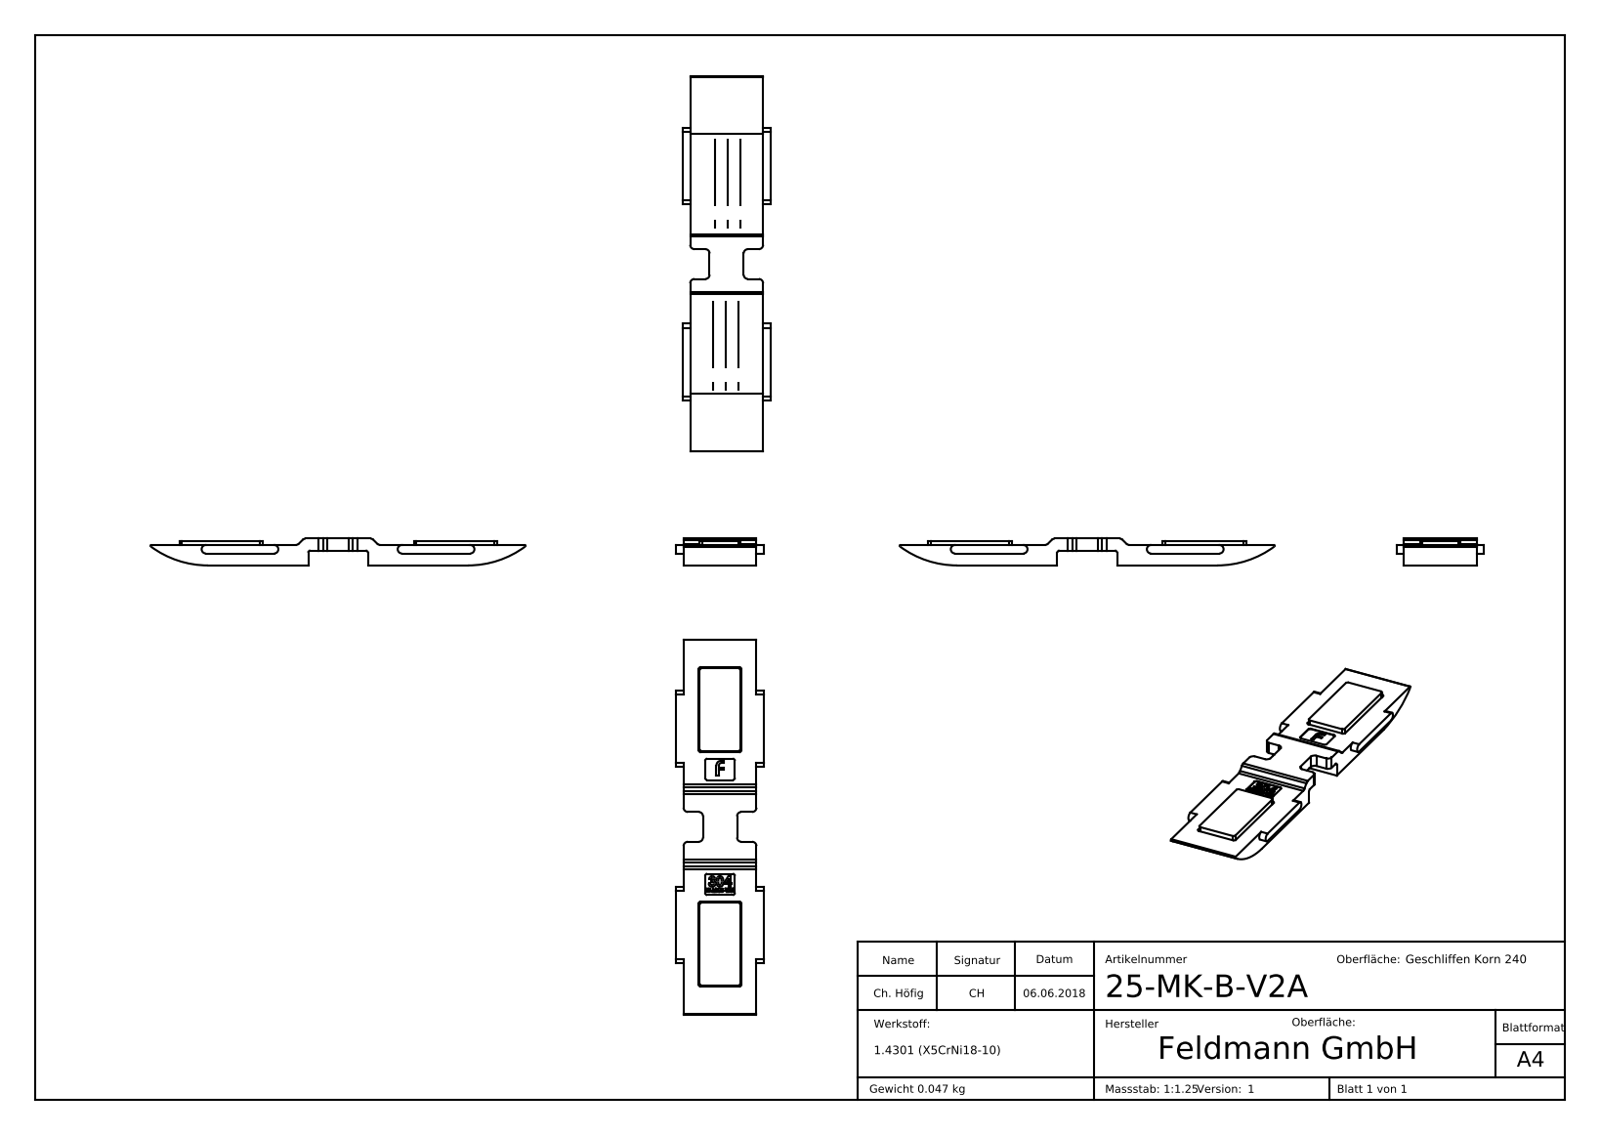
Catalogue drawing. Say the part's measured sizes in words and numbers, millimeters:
The part is named "25-MK-B-XXX Teil1_25-MK-B-V2A Teil1; 25-MK-B-XXX Teil2_25-MK-B-XXX Teil2; 25-MK-B-V2A". Its 3-D file was written by "SolidWorks 2015 (CONFIG_CONTROL_DESIGN)". It is 3 solids with 296 faces: 188 planar, 54 cylindrical and 54 other. Overall it measures 88 by 20.5 by 6.3 millimeters. Its volume is 6 566 cubic millimeters and its surface area 5 176 square millimeters. Partial cylindrical surfaces (rounded edges, fillets, slot ends): 26 of radius 0.5, 16 of radius 1, 2 of radius 0.2, 2 of radius 22.5. The main face-to-face distances are 1, 3.8, 4.8, 2, 5.8, 3.5, 2.8, 17.1, 1.5, 0.5.
